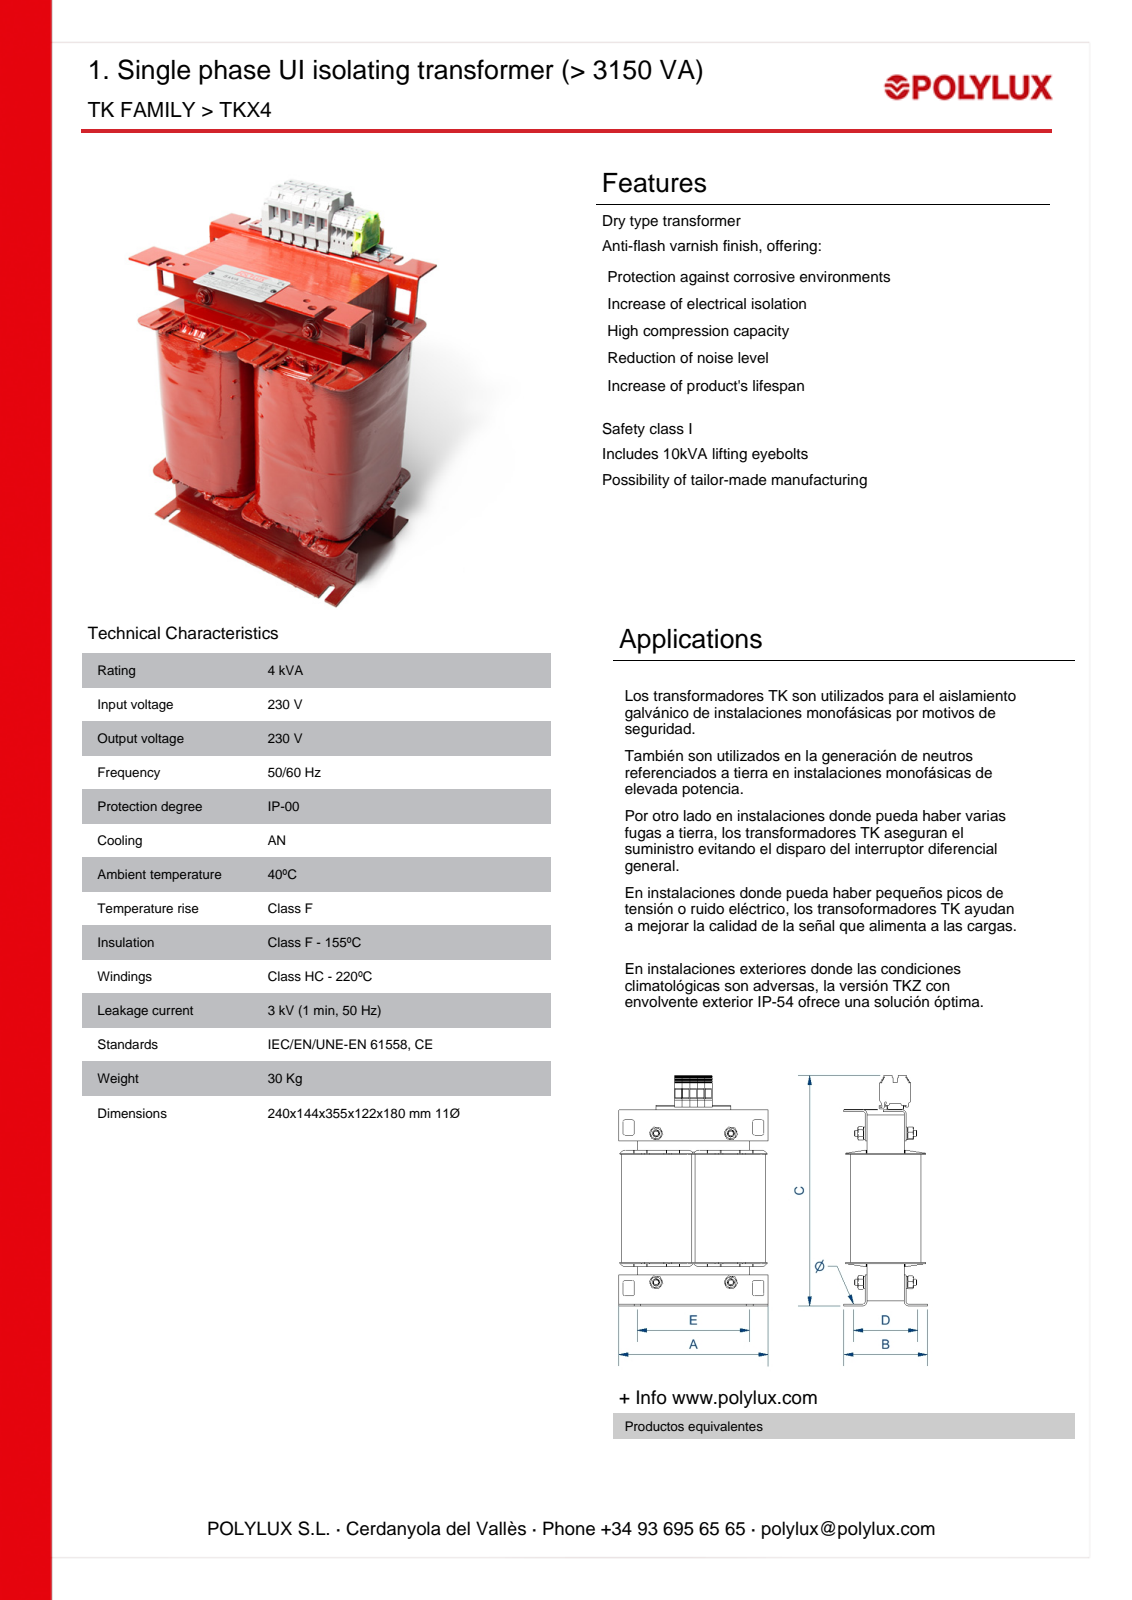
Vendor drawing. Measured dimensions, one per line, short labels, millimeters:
name: TKX4
written by: Autodesk Inventor 2018 (AUTOMOTIVE_DESIGN)
unit: mm
bodies: 32 solids, 1739 faces (1258 planar, 457 cylindrical, 24 other)
size: 371.3 × 240 × 144
volume: 6 714 000 mm³; area: 1 022 000 mm²
holes: 10× ⌀6.4, 6× ⌀3.5, 6× ⌀7, 4× ⌀6.65, 4× ⌀8.4, 4× ⌀10, 4× ⌀12, 3× ⌀9, 1× ⌀3, 1× ⌀5.8
bosses: 4× ⌀16, 4× ⌀8
rounds: 51× R0.5, 24× R10, 20× R3, 12× R1, 10× R2, 8× R4, 6× R0.2, 6× R0.3
face distances: 3, 120, 23.5, 2, 26.5, 73, 1, 96.5, 25.5, 63
hole spacings: 12, 23.62, 38, 39.46, 77.23, 116, 73, 20.35
